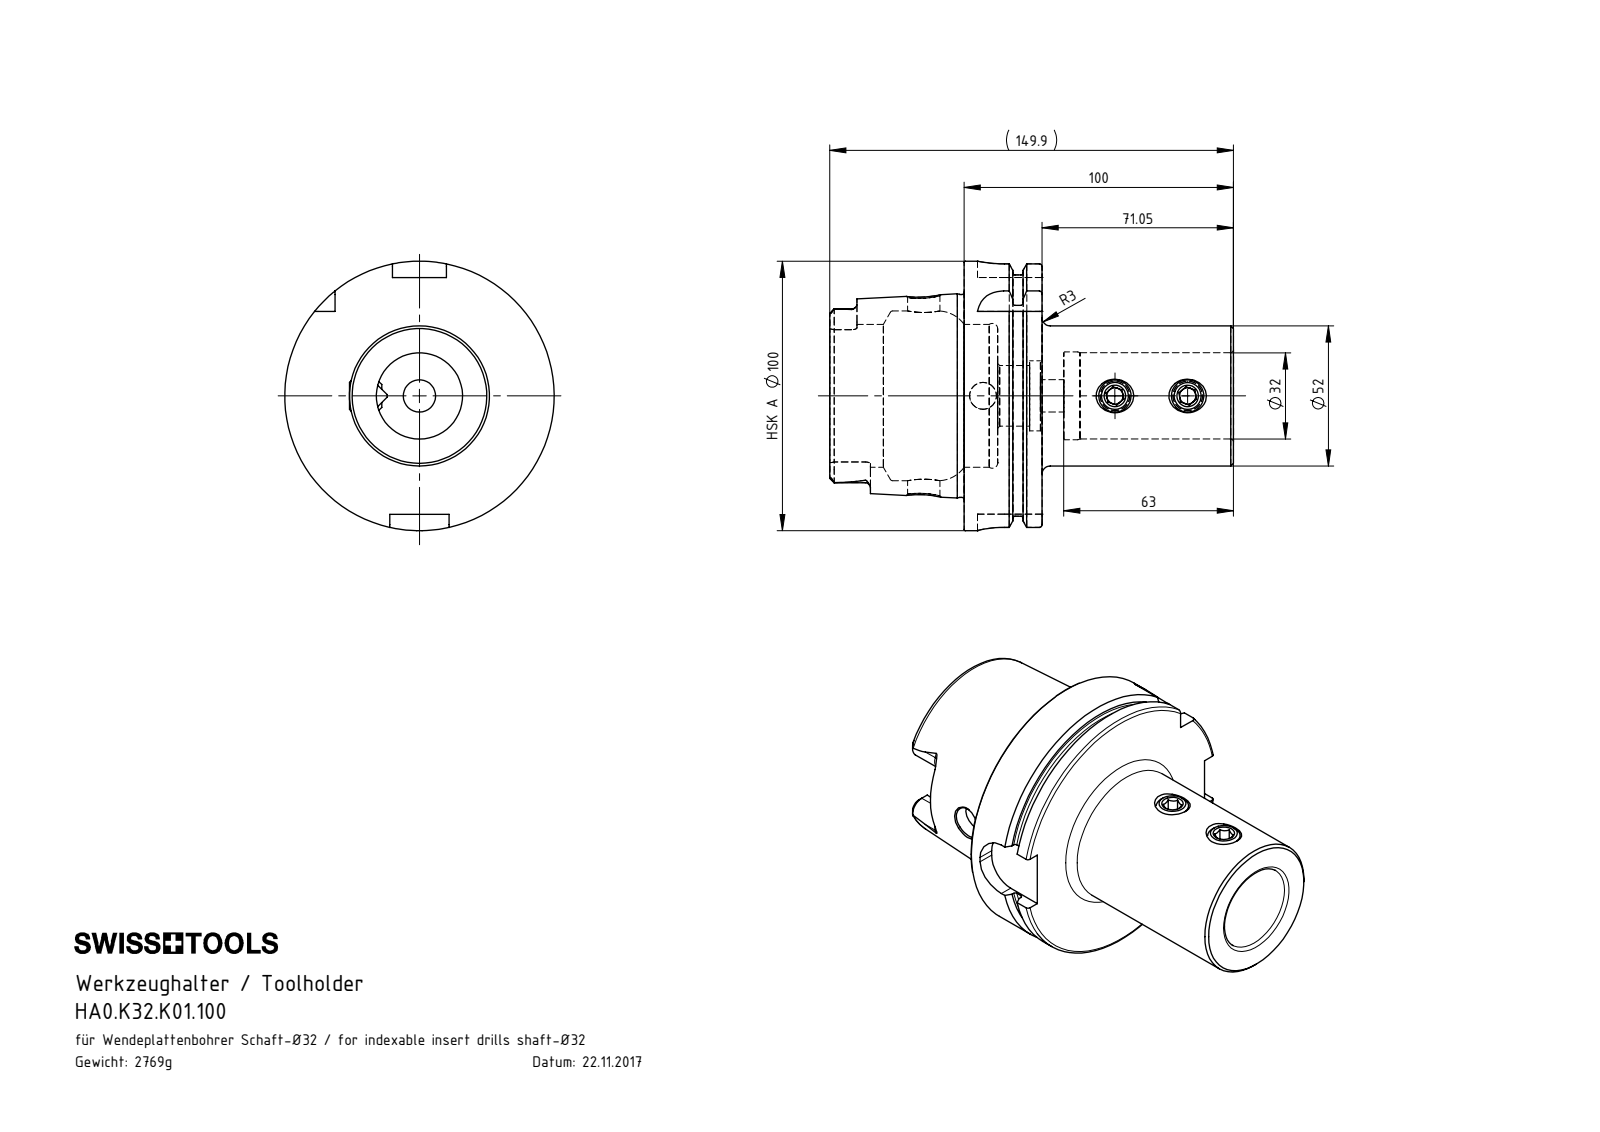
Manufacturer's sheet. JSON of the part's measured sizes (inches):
{"part_name": "HA0-K32.K01.100; K32-ER2.012.014_PreviewCfg; HA0-K32.K01.100_A_Fertigbearbeitung; K32-ER1.012.012", "step_written_by": "SolidWorks 2017 (CONFIG_CONTROL_DESIGN)", "units": "inches", "bodies": {"solids": 3, "faces": 224, "planar": 69, "cylindrical": 62, "other": 93}, "overall_size": [5.902, 3.937, 3.937], "volume_in3": 21.52, "surface_area_in2": 107.2, "round_holes": [[0.236, 2], [0.433, 2], [0.472, 2], [0.394, 1], [0.886, 1], [1.024, 1], [1.26, 1], [1.283, 1], [2.087, 1], [2.48, 1]], "round_bosses_or_shafts": [[0.472, 2], [3.937, 1], [3.62, 1], [2.963, 1], [2.047, 1]], "partial_cylinders_radius": [[0.075, 6], [0.394, 4], [0.19, 2], [0.192, 2]], "face_to_face_distances": [1.14, 0.49, 0.65, 3.937, 3.447, 2.797, 1.965, 2.455, 3.104, 5.902], "hole_center_spacings": [1.063, 1.929, 2.992]}
